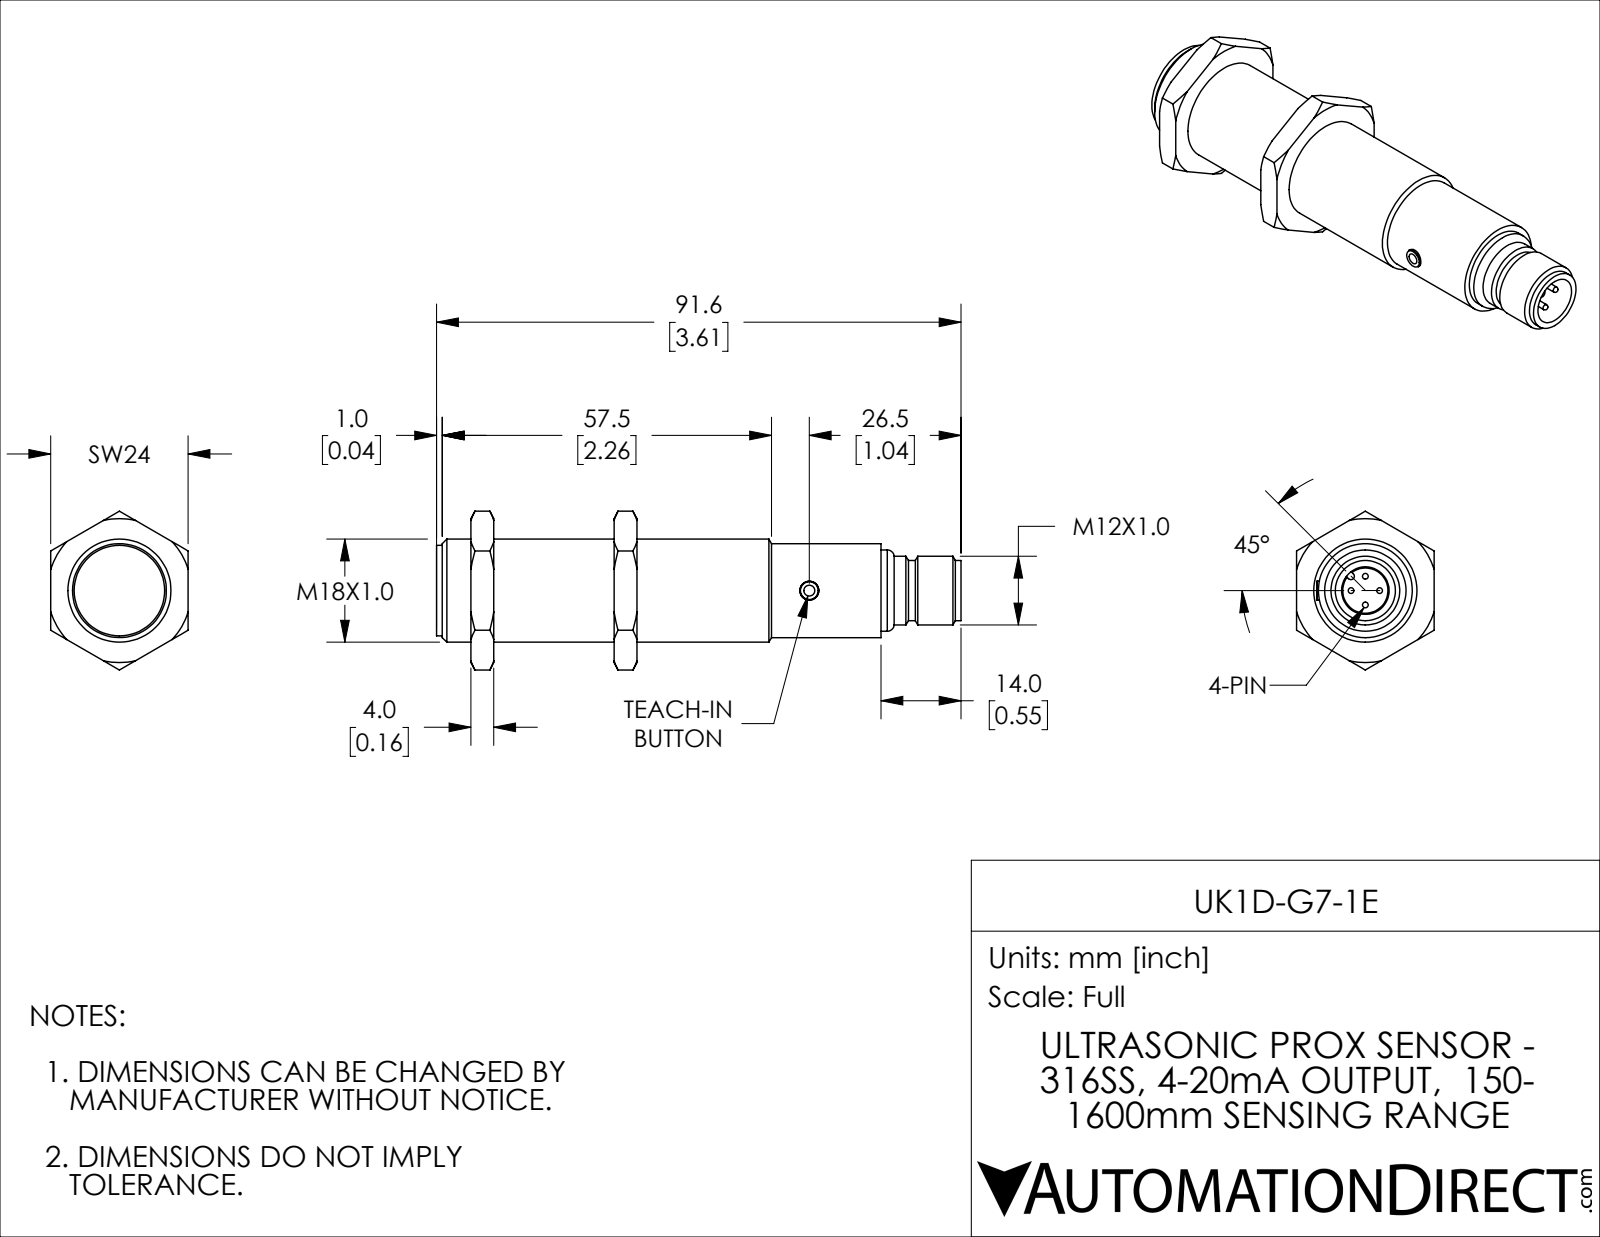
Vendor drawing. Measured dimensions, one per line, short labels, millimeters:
name: UK1D-G7-1E
written by: SolidWorks 2018 (AUTOMOTIVE_DESIGN)
unit: mm
bodies: 4 solids, 113 faces (27 planar, 35 cylindrical, 51 other)
size: 91.6 × 27.7 × 24
volume: 21 930 mm³; area: 7 723 mm²
holes: 1× ⌀3.3, 1× ⌀8.3, 1× ⌀18
bosses: 4× ⌀1, 1× ⌀16.4, 1× ⌀15.8, 1× ⌀14.2, 1× ⌀12, 1× ⌀10.5
rounds: 1× R0.6
face distances: 25, 4, 24, 29, 21, 6, 10, 31, 35, 77.6
